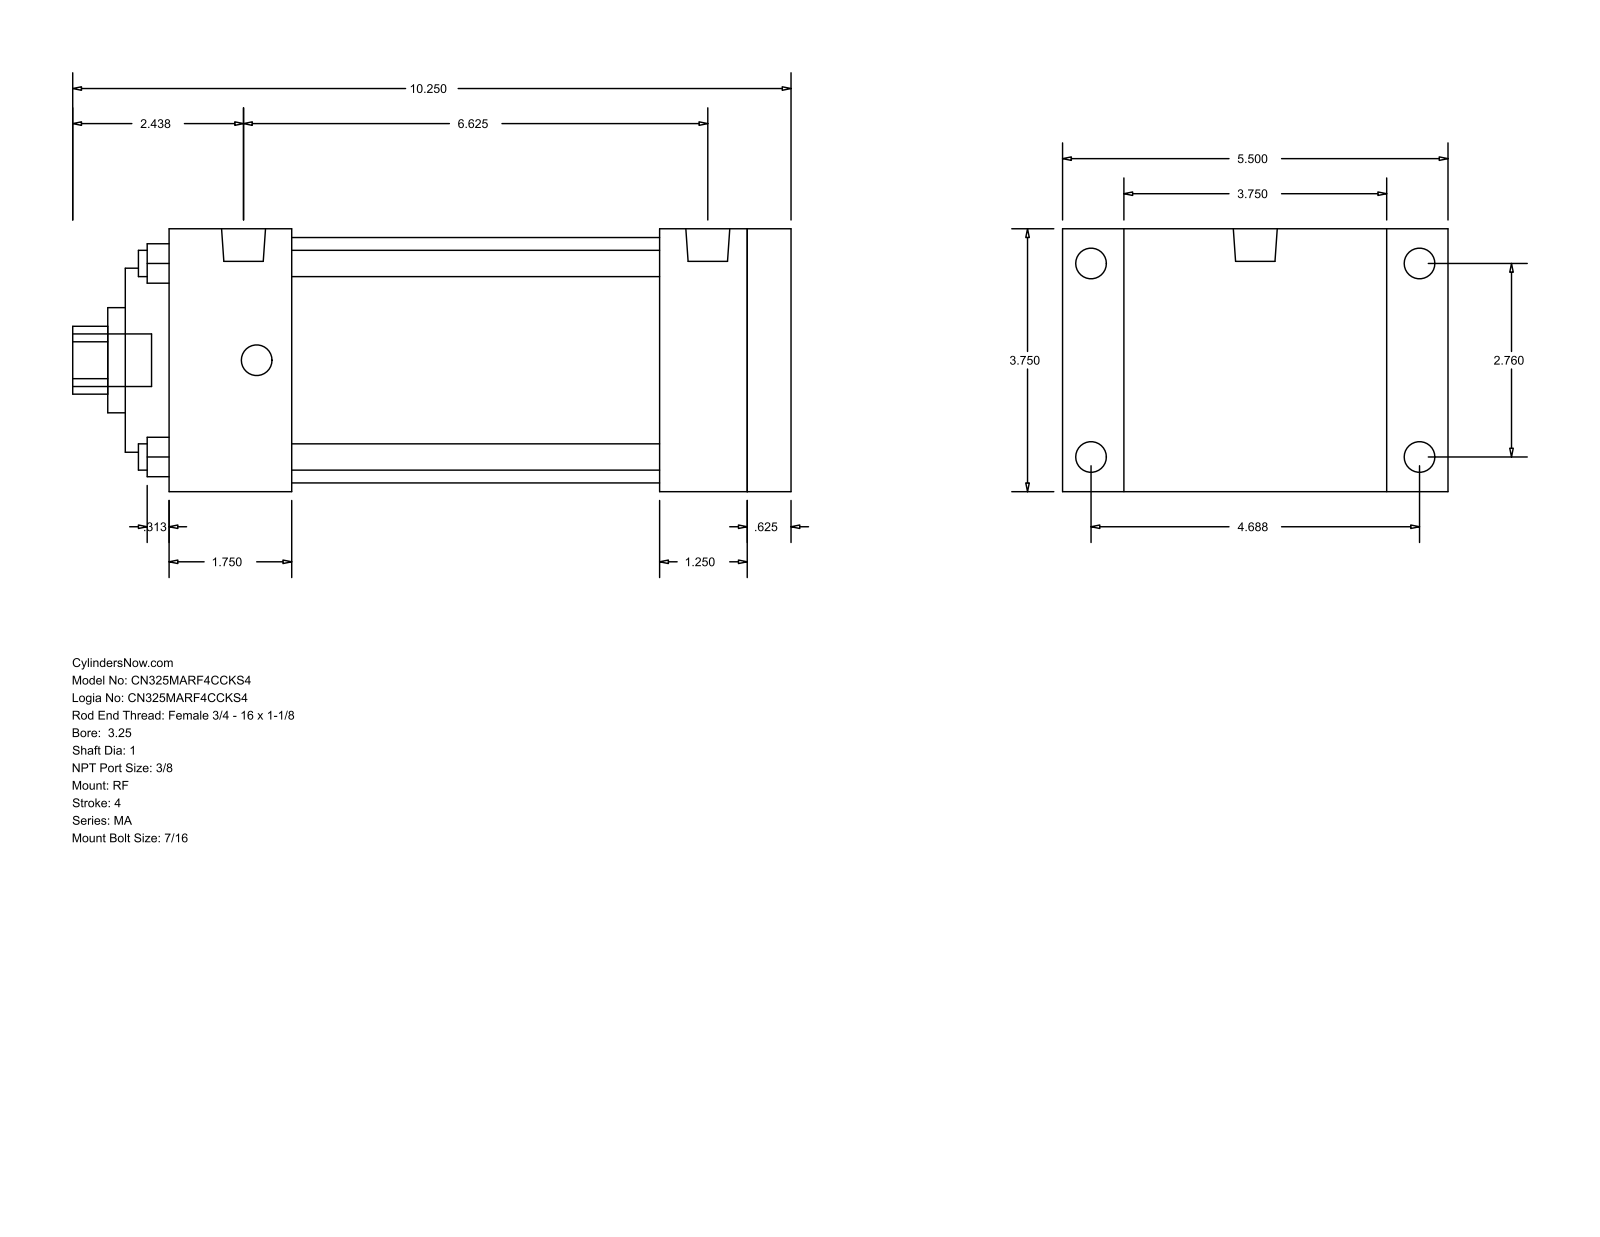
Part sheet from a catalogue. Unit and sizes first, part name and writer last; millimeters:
Units: millimetres
Overall size (bounding box): 260.35 × 139.7 × 95.25
Round holes (diameter × count): ⌀9.53 ×4, ⌀25.4 ×1, ⌀38.1 ×1, ⌀66.67 ×1, ⌀88.9 ×1
Round bosses / shafts (diameter × count): ⌀11.11 ×8, ⌀15.93 ×2, ⌀19.05 ×1
Partial cylindrical surfaces — rounded edges, fillets, slot ends (radius × count): R12.29 ×1
Main face-to-face distances: 95.24, 225.43, 209.55, 15.88, 22.23, 117.47, 15.87, 177.8, 31.75, 47.63
Hole centre spacings: 49.57, 70.1, 99.14
Bodies: 0 solids, 94 faces (65 planar, 29 cylindrical, 0 other)
Part name (STEP PRODUCT): MA_RF__0325_1
STEP written by: GSSL Pune (CONFIG_CONTROL_DESIGN)
